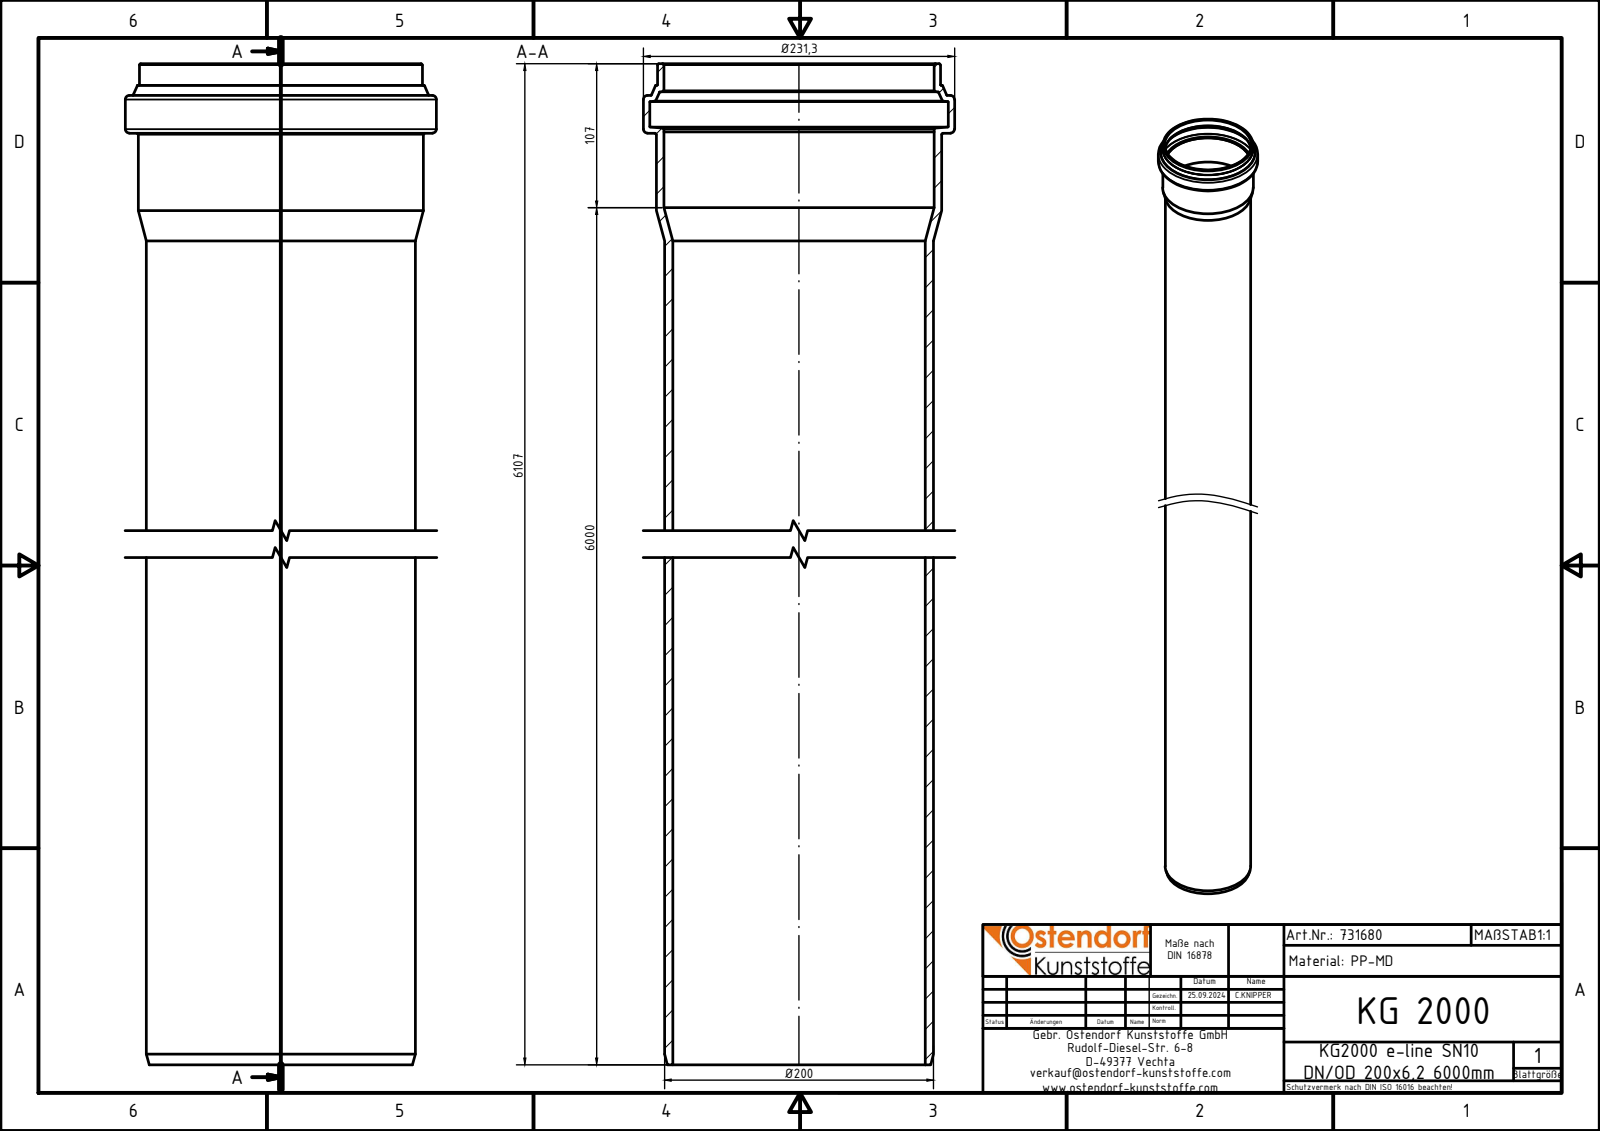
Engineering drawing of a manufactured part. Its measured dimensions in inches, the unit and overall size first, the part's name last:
Units: inches
Overall size (bounding box): 240.433 × 9.106 × 9.106
Round holes (diameter × count): ⌀7.386 ×1, ⌀7.906 ×1, ⌀7.913 ×1, ⌀8.736 ×1
Round bosses / shafts (diameter × count): ⌀9.106 ×1, ⌀8.346 ×1, ⌀8.283 ×1, ⌀7.874 ×1
Main face-to-face distances: 238.398, 239.508, 1.11, 240.433, 2.035, 0.925, 239.802, 1.404, 0.294, 0.631
Volume: 1 407 in³ · Surface area: 11 590 in²
Bodies: 1 solid, 37 faces (6 planar, 9 cylindrical, 22 other)
Part name (STEP PRODUCT): 731680z
STEP written by: Autodesk Inventor 2024 (AUTOMOTIVE_DESIGN)
